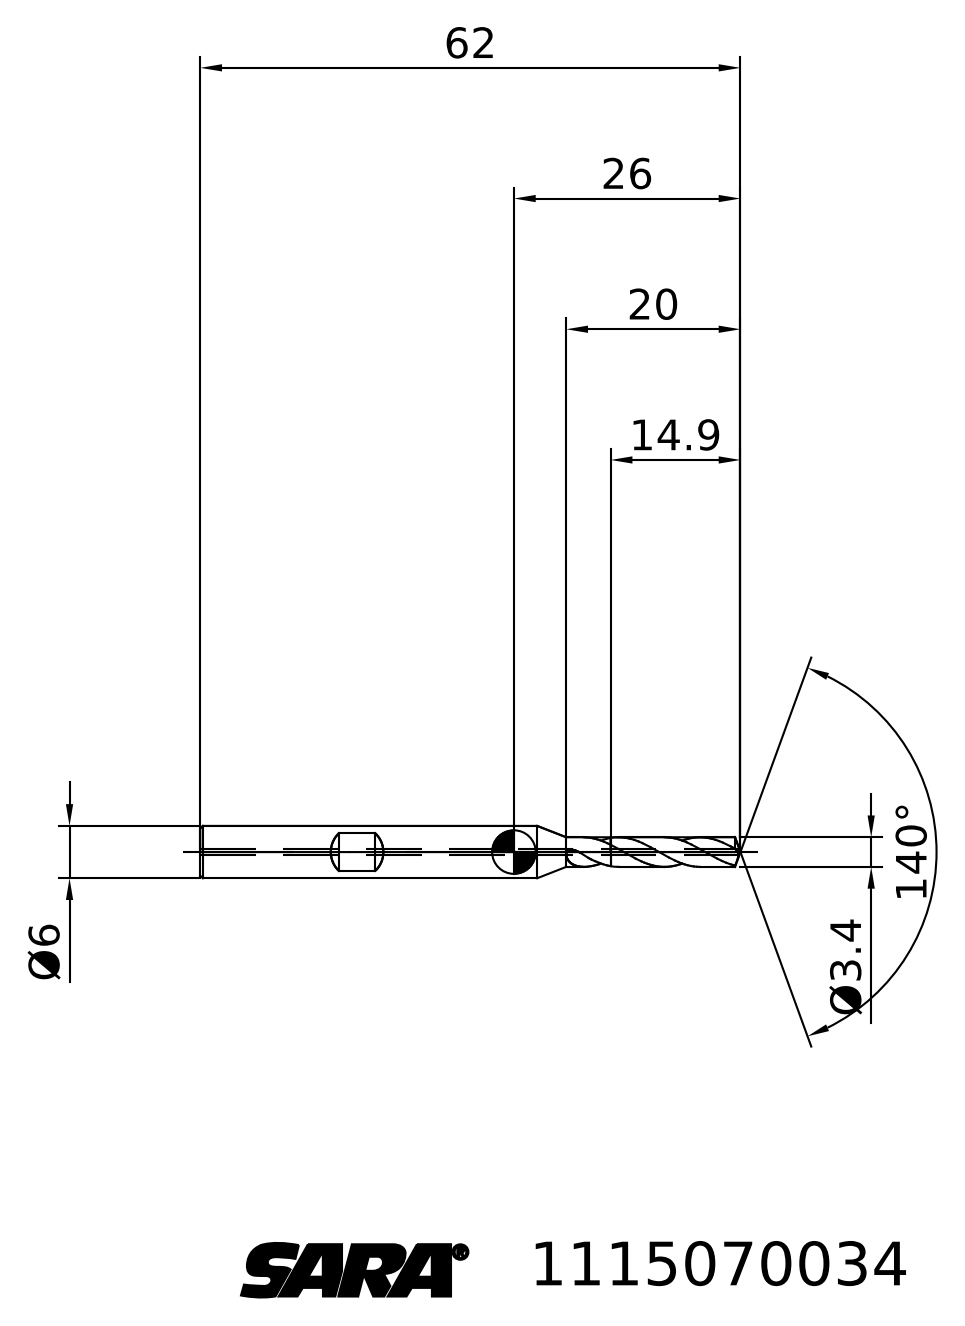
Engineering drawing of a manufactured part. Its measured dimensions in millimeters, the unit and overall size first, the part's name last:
Units: millimetres
Overall size (bounding box): 62 × 6 × 6
Main face-to-face distances: 47.1
Volume: 1 258 mm³ · Surface area: 1 051 mm²
Bodies: 2 solids, 29 faces (6 planar, 0 cylindrical, 23 other)
STEP written by: TDM (AUTOMOTIVE_DESIGN)
